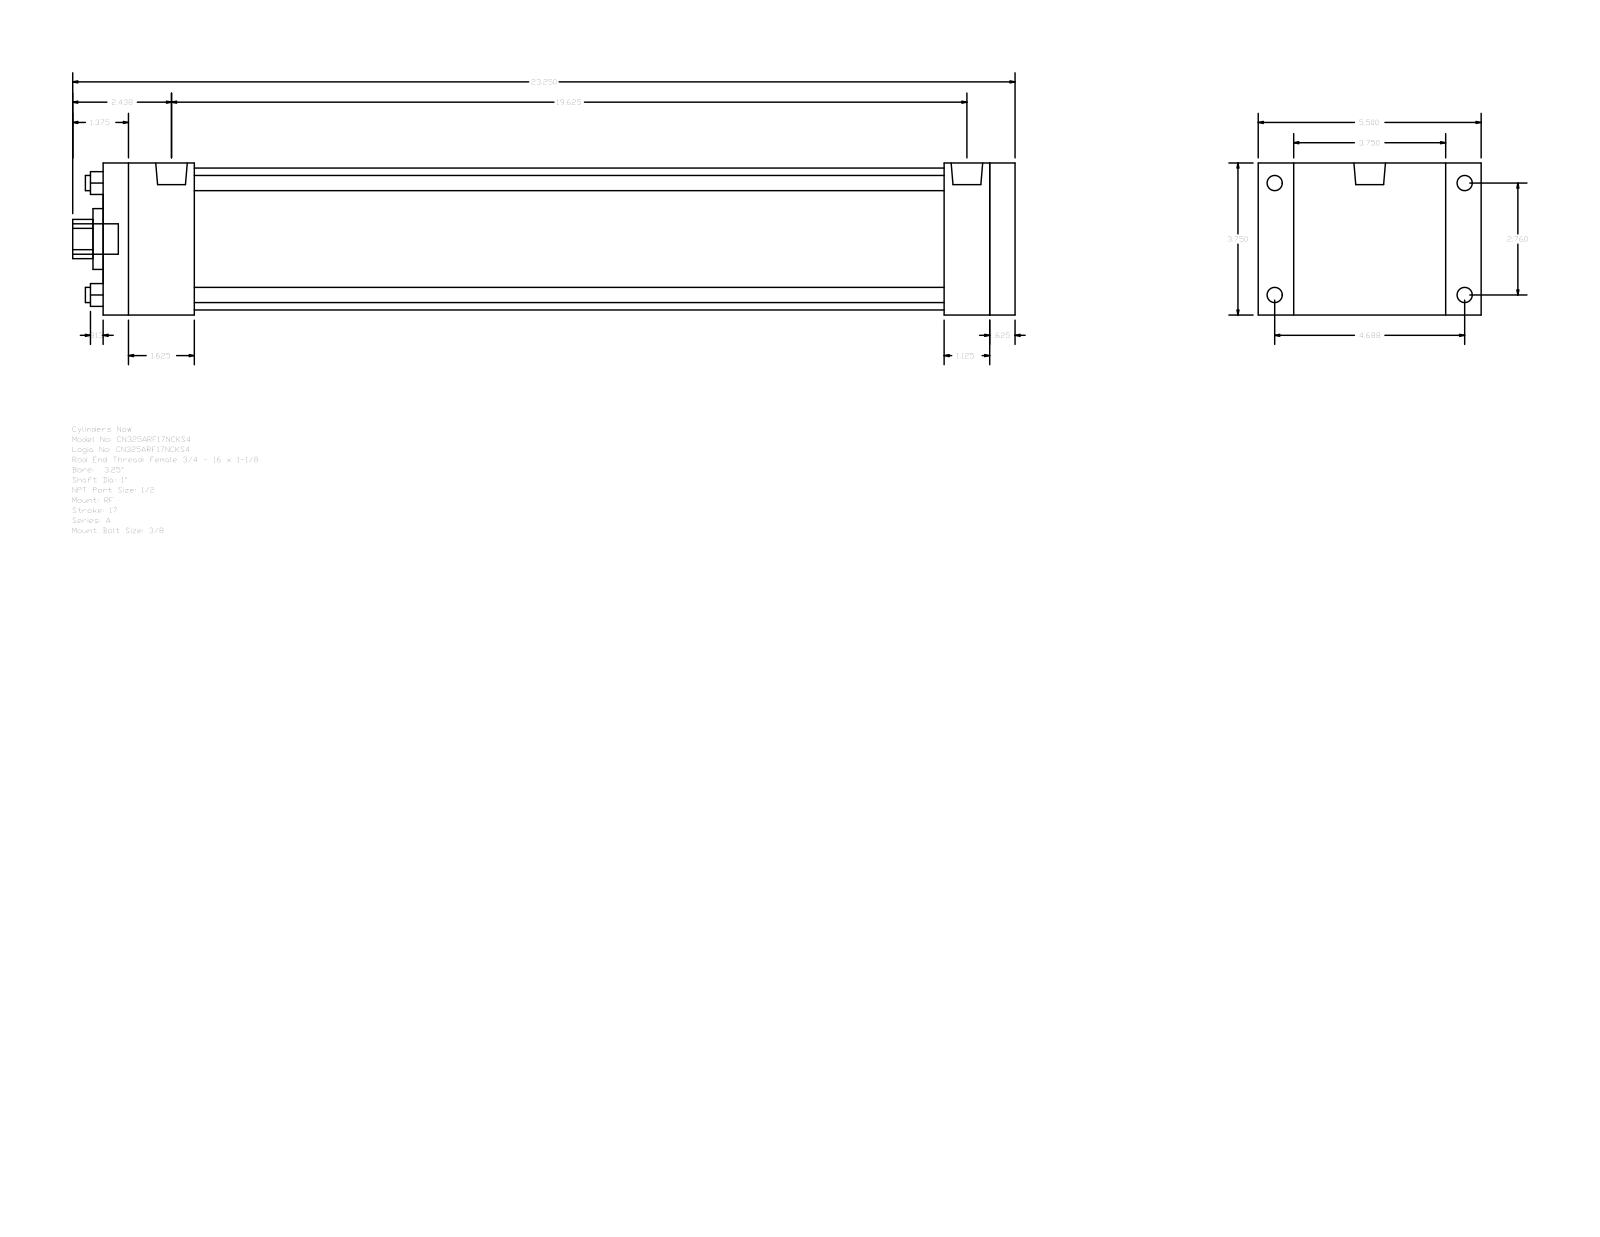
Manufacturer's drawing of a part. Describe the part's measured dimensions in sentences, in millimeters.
The part is named "A_RF__0325_1". Its 3-D file was written by "GSSL Pune (CONFIG_CONTROL_DESIGN)". It is 0 solids with 92 faces: 64 planar, 28 cylindrical and 0 other. Overall it measures 590.55 by 139.7 by 95.25 millimeters. Round holes: 4 of diameter 9.53, 1 of diameter 25.4, 1 of diameter 38.1, 1 of diameter 88.9. Round bosses or shafts: 4 of diameter 9.53, 4 of diameter 8.73, 2 of diameter 19.77, 1 of diameter 19.05. Partial cylindrical surfaces (rounded edges, fillets, slot ends): 1 of radius 12.29. The main face-to-face distances are 95.24, 571.5, 555.62, 15.88, 22.23, 117.47, 28.57, 527.05, 44.45, 57.15. The hole center spacings are 49.57, 70.1, 99.14.
